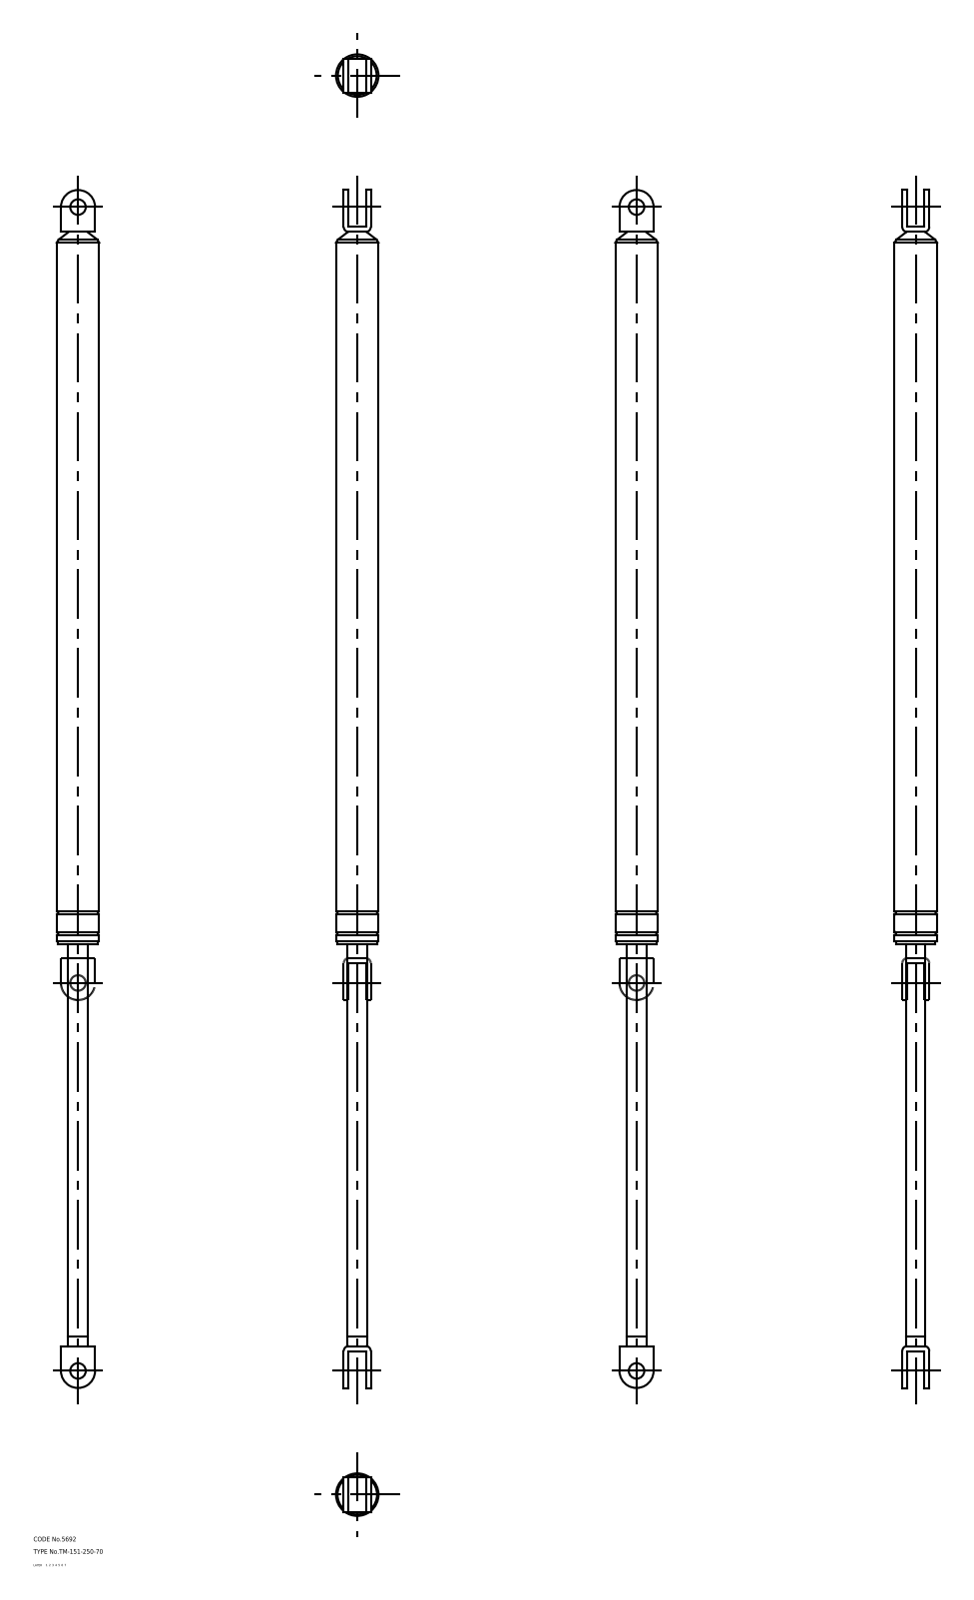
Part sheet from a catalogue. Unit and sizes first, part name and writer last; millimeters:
Units: millimetres
Overall size (bounding box): 772 × 27.4 × 27.4
Round holes (diameter × count): ⌀10 ×2
Round bosses / shafts (diameter × count): ⌀27.4 ×1, ⌀25.5 ×1, ⌀12.5 ×1
Partial cylindrical surfaces — rounded edges, fillets, slot ends (radius × count): R3 ×4, R11 ×2
Main face-to-face distances: 3.2, 14.2, 17.4, 11, 721.2, 22, 262.2, 724.4, 462.2, 459
Hole centre spacings: 750
Volume: 307 737 mm³ · Surface area: 56 327 mm²
Bodies: 2 solids, 63 faces (21 planar, 30 cylindrical, 12 other)
Part name (STEP PRODUCT): body_div
STEP written by: spGate 16.7.1 (AUTOMOTIVE_DESIGN)
